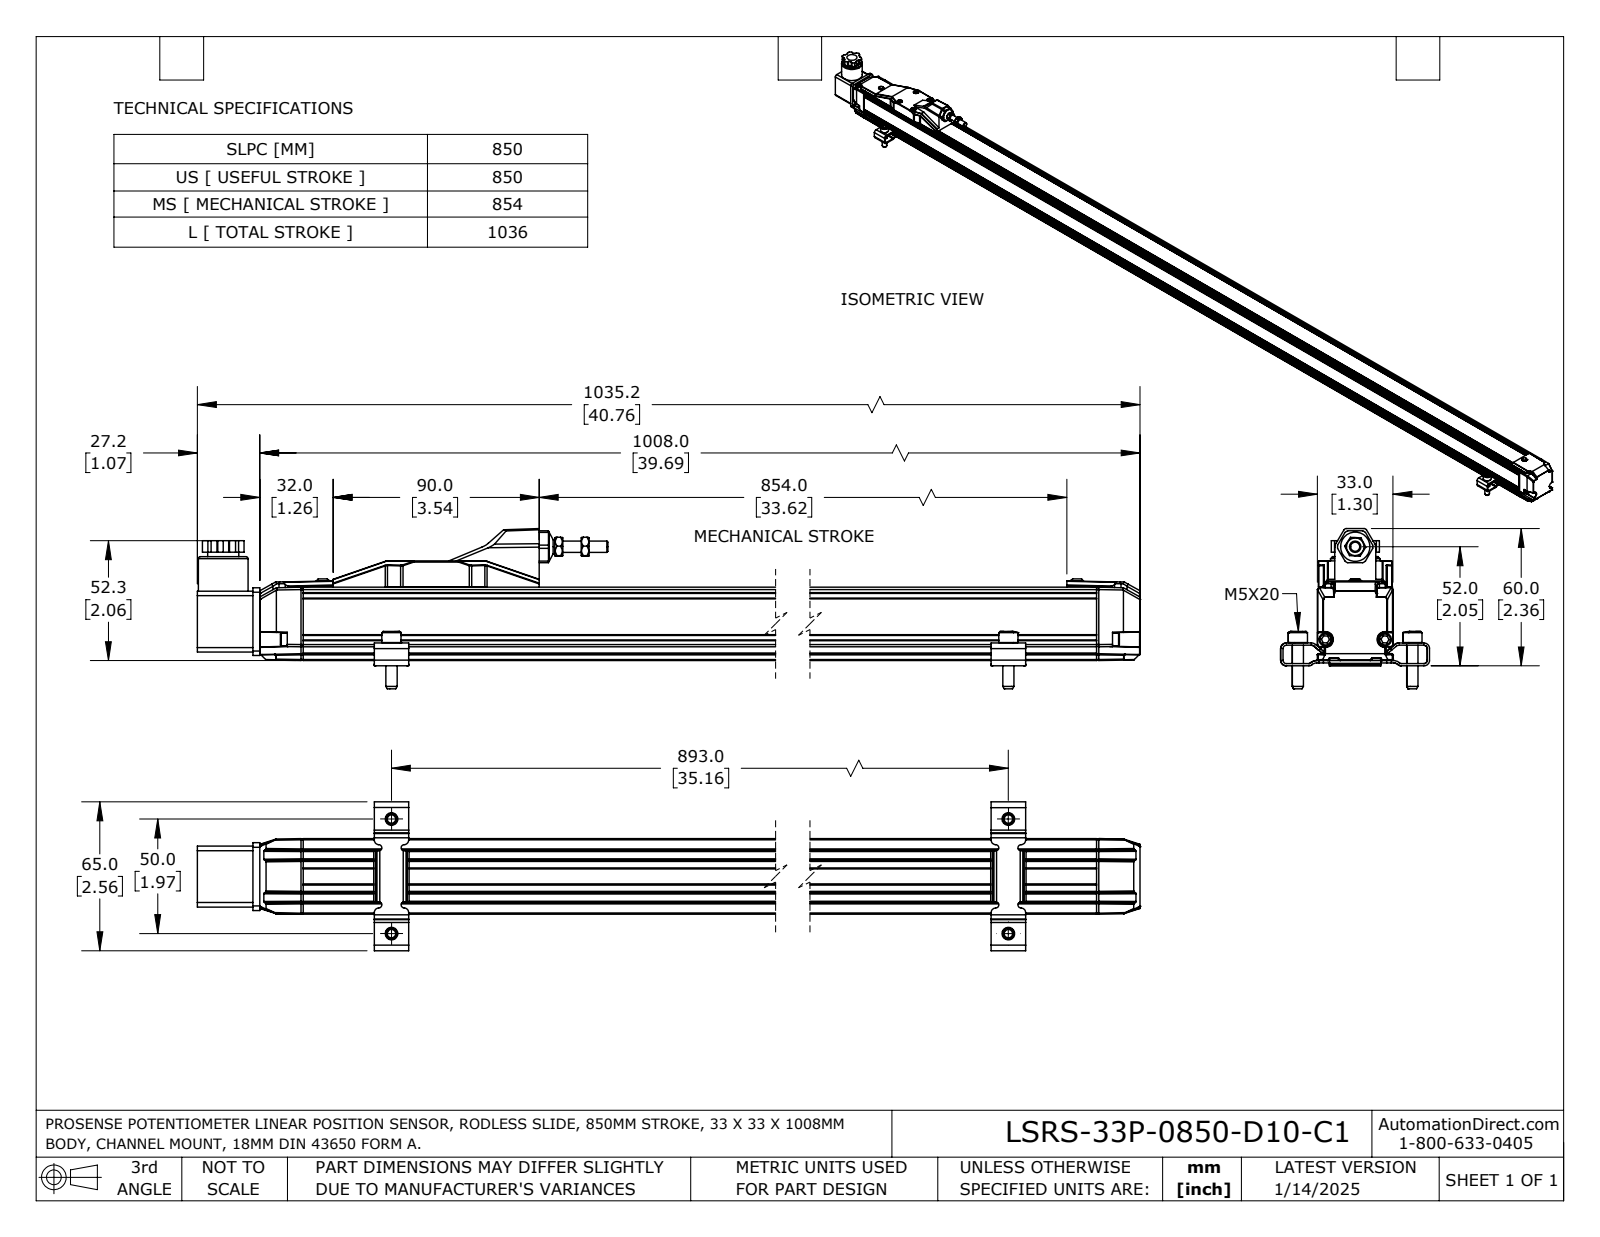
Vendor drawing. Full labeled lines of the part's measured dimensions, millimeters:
Part name (STEP PRODUCT): LSRS-33P-0850-D10-C1
STEP written by: SolidWorks 2023 (AUTOMOTIVE_DESIGN)
Units: millimetres
Bodies: 10 solids, 1310 faces (821 planar, 357 cylindrical, 132 other)
Overall size (bounding box): 1035.2 × 70 × 65
Volume: 980 800 mm³ · Surface area: 225 400 mm²
Round holes (diameter × count): ⌀4.7 ×4, ⌀5.5 ×4, ⌀2.7 ×2, ⌀3.3 ×2, ⌀4 ×1, ⌀5 ×1, ⌀5.3 ×1, ⌀5.9 ×1, ⌀6 ×1, ⌀7 ×1, ⌀10 ×1, ⌀10.5 ×1
Round bosses / shafts (diameter × count): ⌀8.4 ×4, ⌀4.9 ×4, ⌀4.6 ×4, ⌀2.9 ×4, ⌀5.6 ×2, ⌀5.5 ×2, ⌀3 ×2, ⌀2.5 ×2
Partial cylindrical surfaces — rounded edges, fillets, slot ends (radius × count): R0.5 ×78, R0.2 ×62, R2 ×44, R3 ×26, R1 ×10, R1.3 ×8, R1.5 ×8, R4 ×8
Main face-to-face distances: 33, 3, 31.6, 29.6, 6, 25.6, 0.9, 0.4, 32.6, 11.3
Hole centre spacings: 15.2, 20, 23.7, 31, 32.7, 42.5, 50, 863.6
